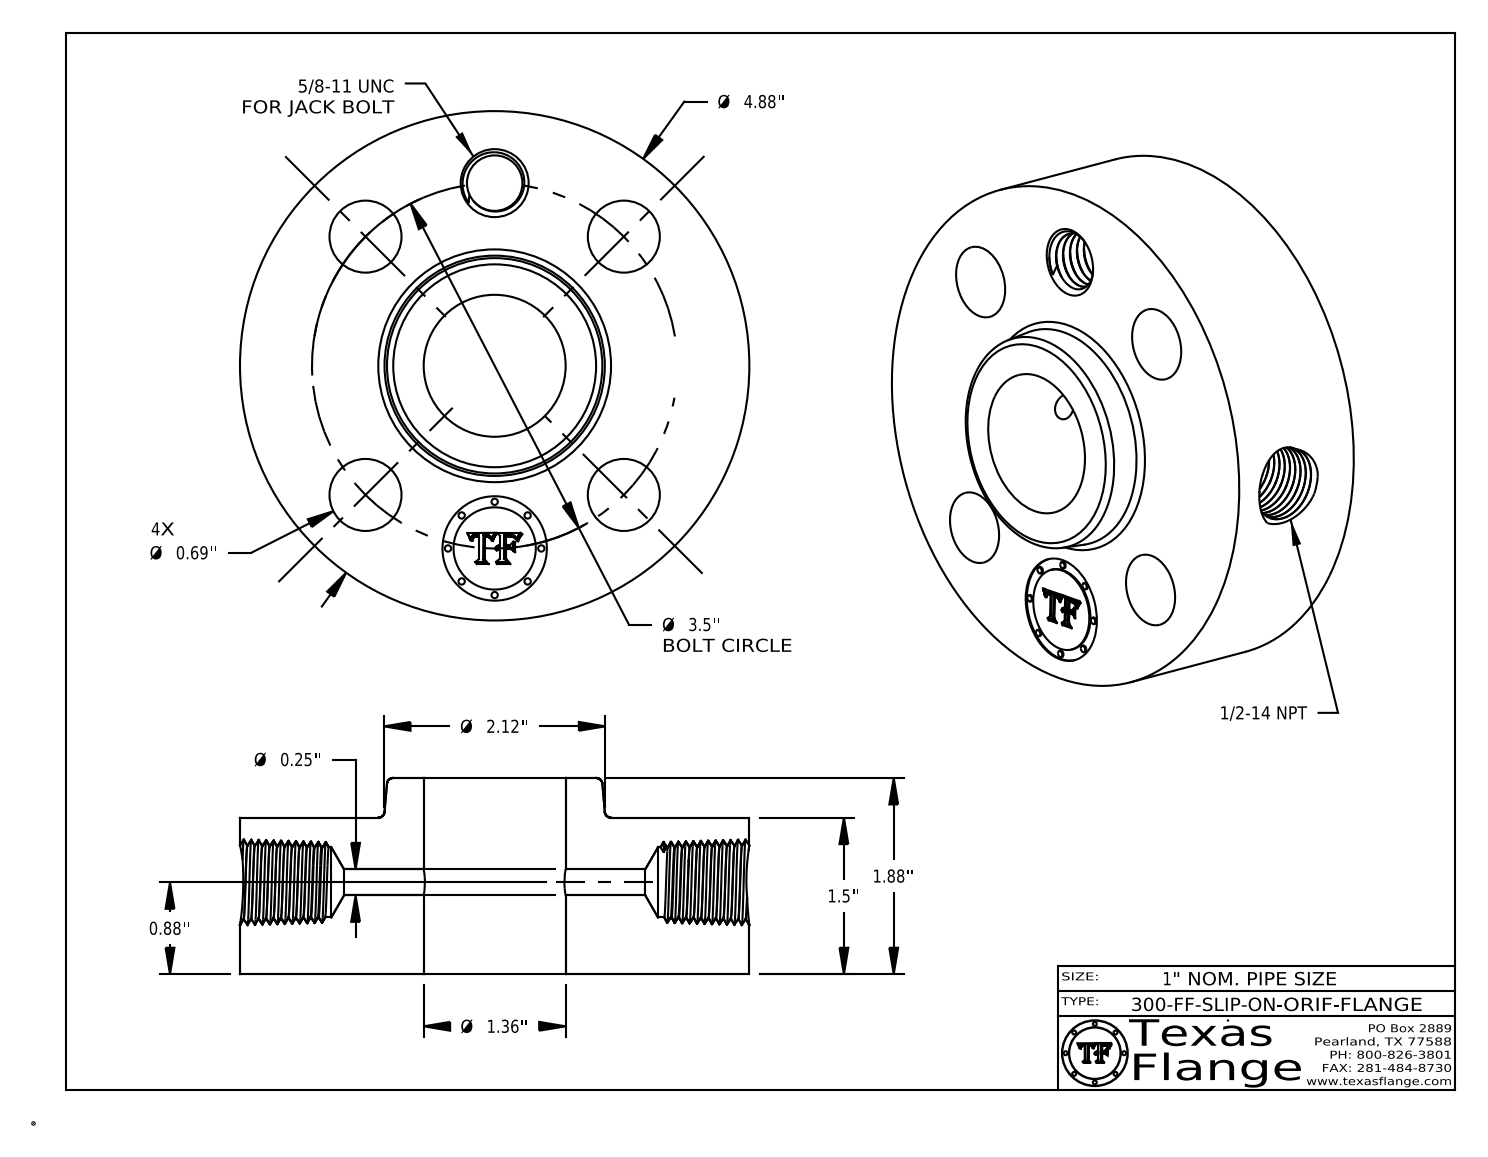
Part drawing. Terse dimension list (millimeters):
name: 300-FF-SLIP-ON
written by: CATIA V5 STEP AP214 (AUTOMOTIVE_DESIGN)
unit: mm
bodies: 1 solid, 759 faces (368 planar, 83 cylindrical, 308 other)
size: 124 × 124 × 47.8
volume: 379 000 mm³; area: 57 480 mm²
holes: 4× ⌀17.5, 1× ⌀6.4, 1× ⌀13.5, 1× ⌀17.1, 1× ⌀25.4, 1× ⌀34.5
bosses: 8× ⌀1.5, 1× ⌀124, 1× ⌀20
face distances: 38.1, 47.8, 9.7, 37.7, 0.4, 10, 7.6, 7.4, 1.4, 6.3
hole spacings: 44.5, 34, 62.9, 82.1, 88.9
